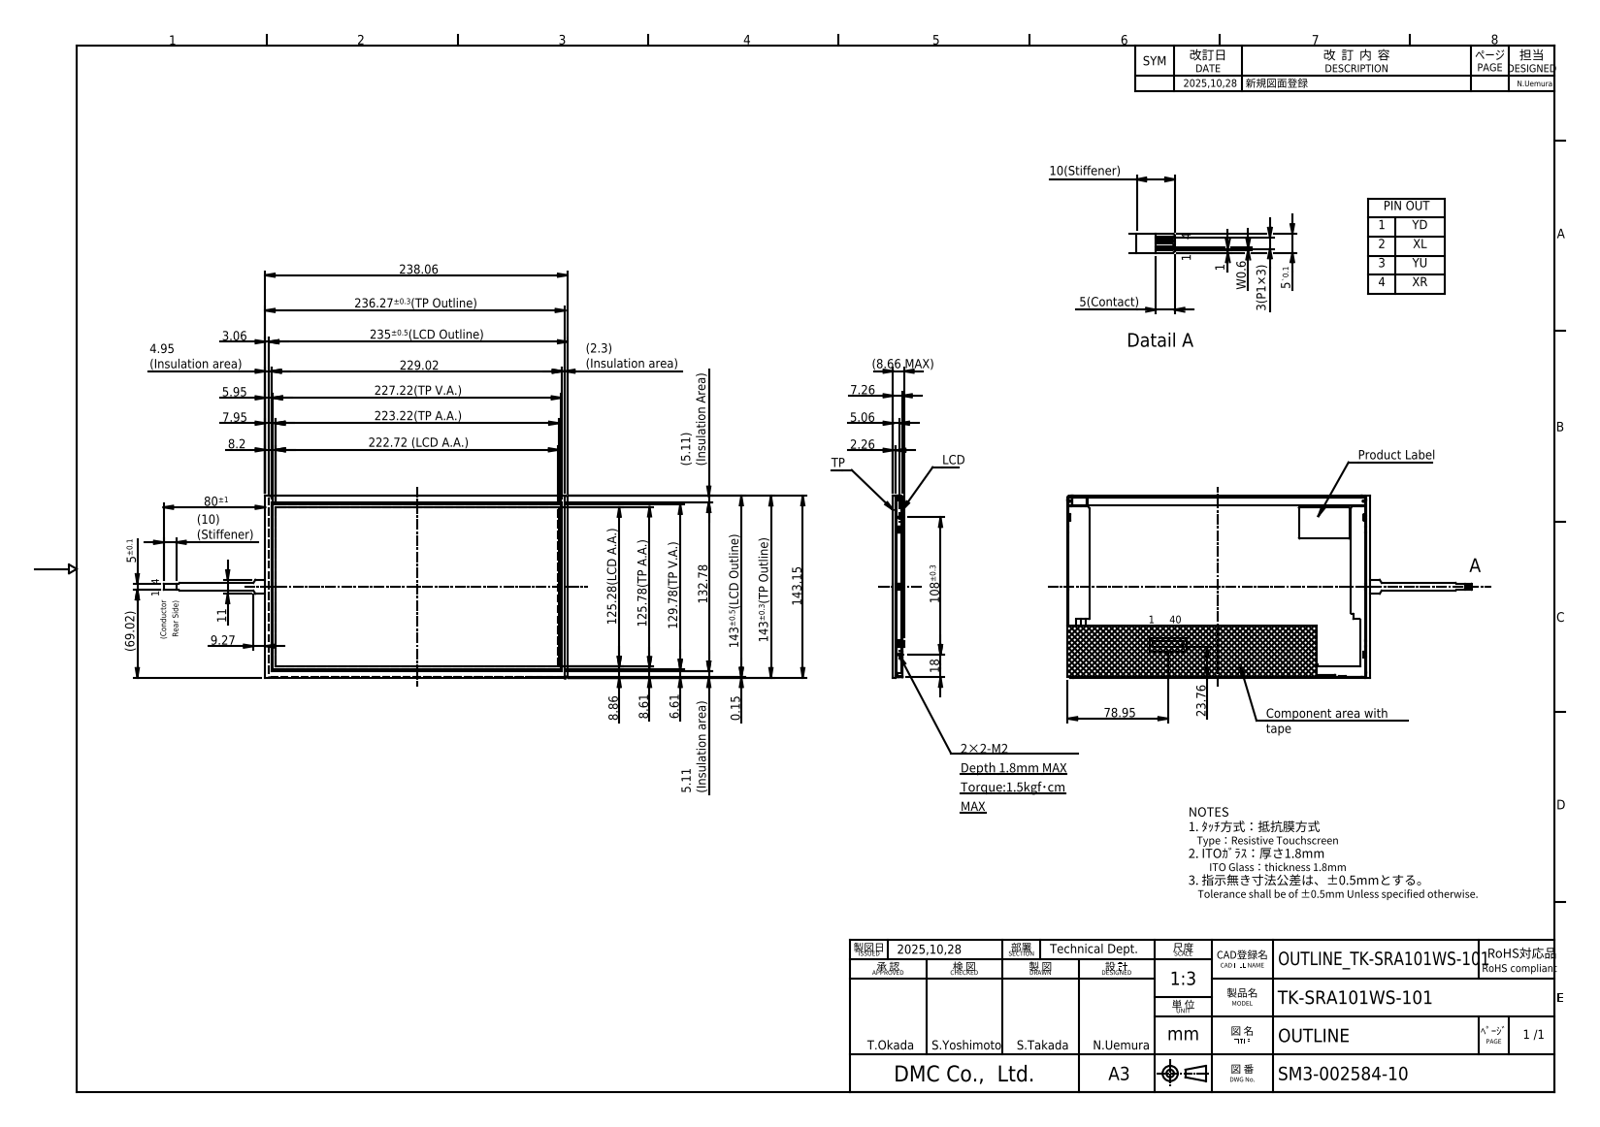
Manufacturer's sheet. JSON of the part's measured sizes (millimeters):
{"part_name": "HP_TK-SRA101WS-101", "step_written_by": "Autodesk Inventor 2024 (AUTOMOTIVE_DESIGN)", "units": "millimeters", "bodies": {"solids": 2, "faces": 844, "planar": 717, "cylindrical": 117, "other": 10}, "overall_size": [318.06, 143.15, 8.77], "volume_mm3": 174158, "surface_area_mm2": 247807, "round_holes": [[1.3, 2], [2, 2]], "round_bosses_or_shafts": [[2.6, 2], [0.8, 1]], "partial_cylinders_radius": [[0.3, 32], [0.5, 16], [0.1, 8], [1, 8], [0.25, 7], [0.6, 4], [0.7, 4], [0.2, 2]], "face_to_face_distances": [2.69, 1.26, 2.1, 0.59, 1.85, 3.95, 3.33, 4.59, 5.23, 4.64], "hole_center_spacings": [108, 231.08]}
